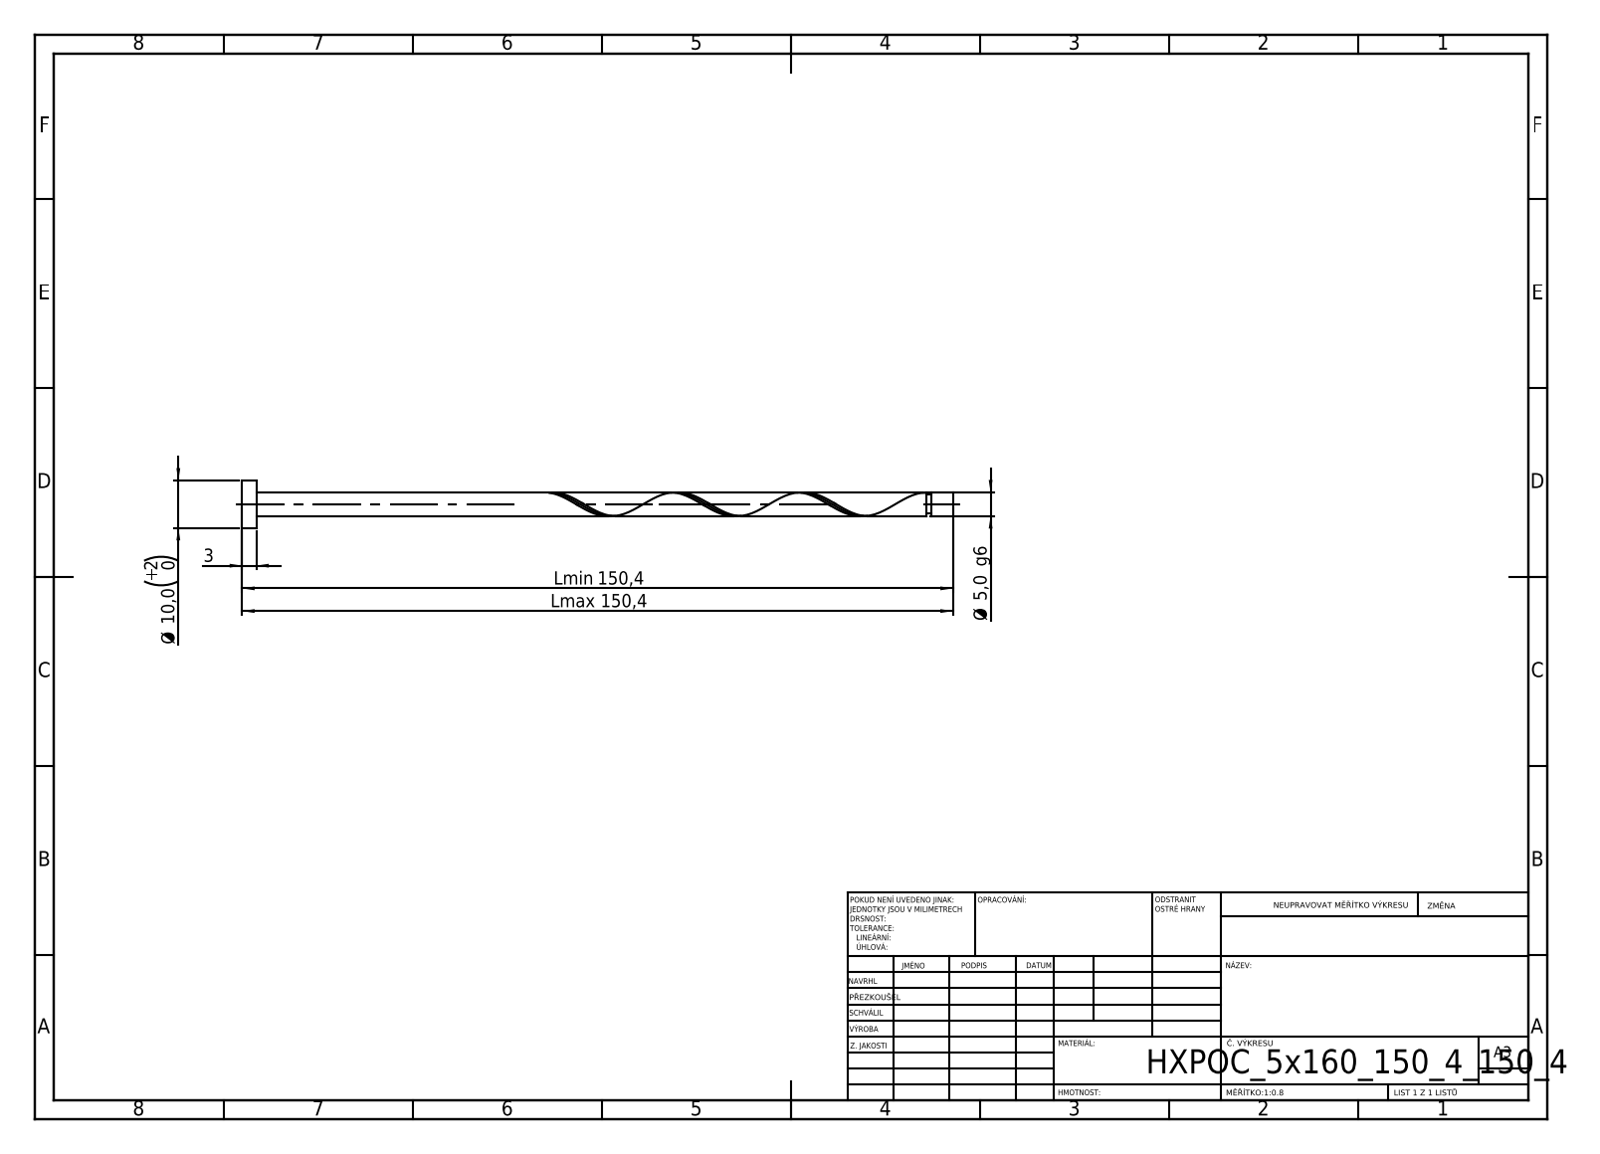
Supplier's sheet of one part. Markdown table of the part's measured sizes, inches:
| quantity | value |
| --- | --- |
| STEP written by | SolidWorks 2019 (CONFIG_CONTROL_DESIGN) |
| units | inches |
| bodies | 1 solid, 21 faces (6 planar, 14 cylindrical, 1 other) |
| overall size | 5.921 × 0.394 × 0.394 |
| volume | 0.189 in³ |
| surface area | 4.067 in² |
| round bosses / shafts (diameter × count) | 0.394 × 1, 0.197 × 1, 0.157 × 1 |
| main face-to-face distances | 0.118, 5.921, 5.803, 5.743, 5.625, 0.178, 5.704, 5.585, 0.039, 0.218 |
